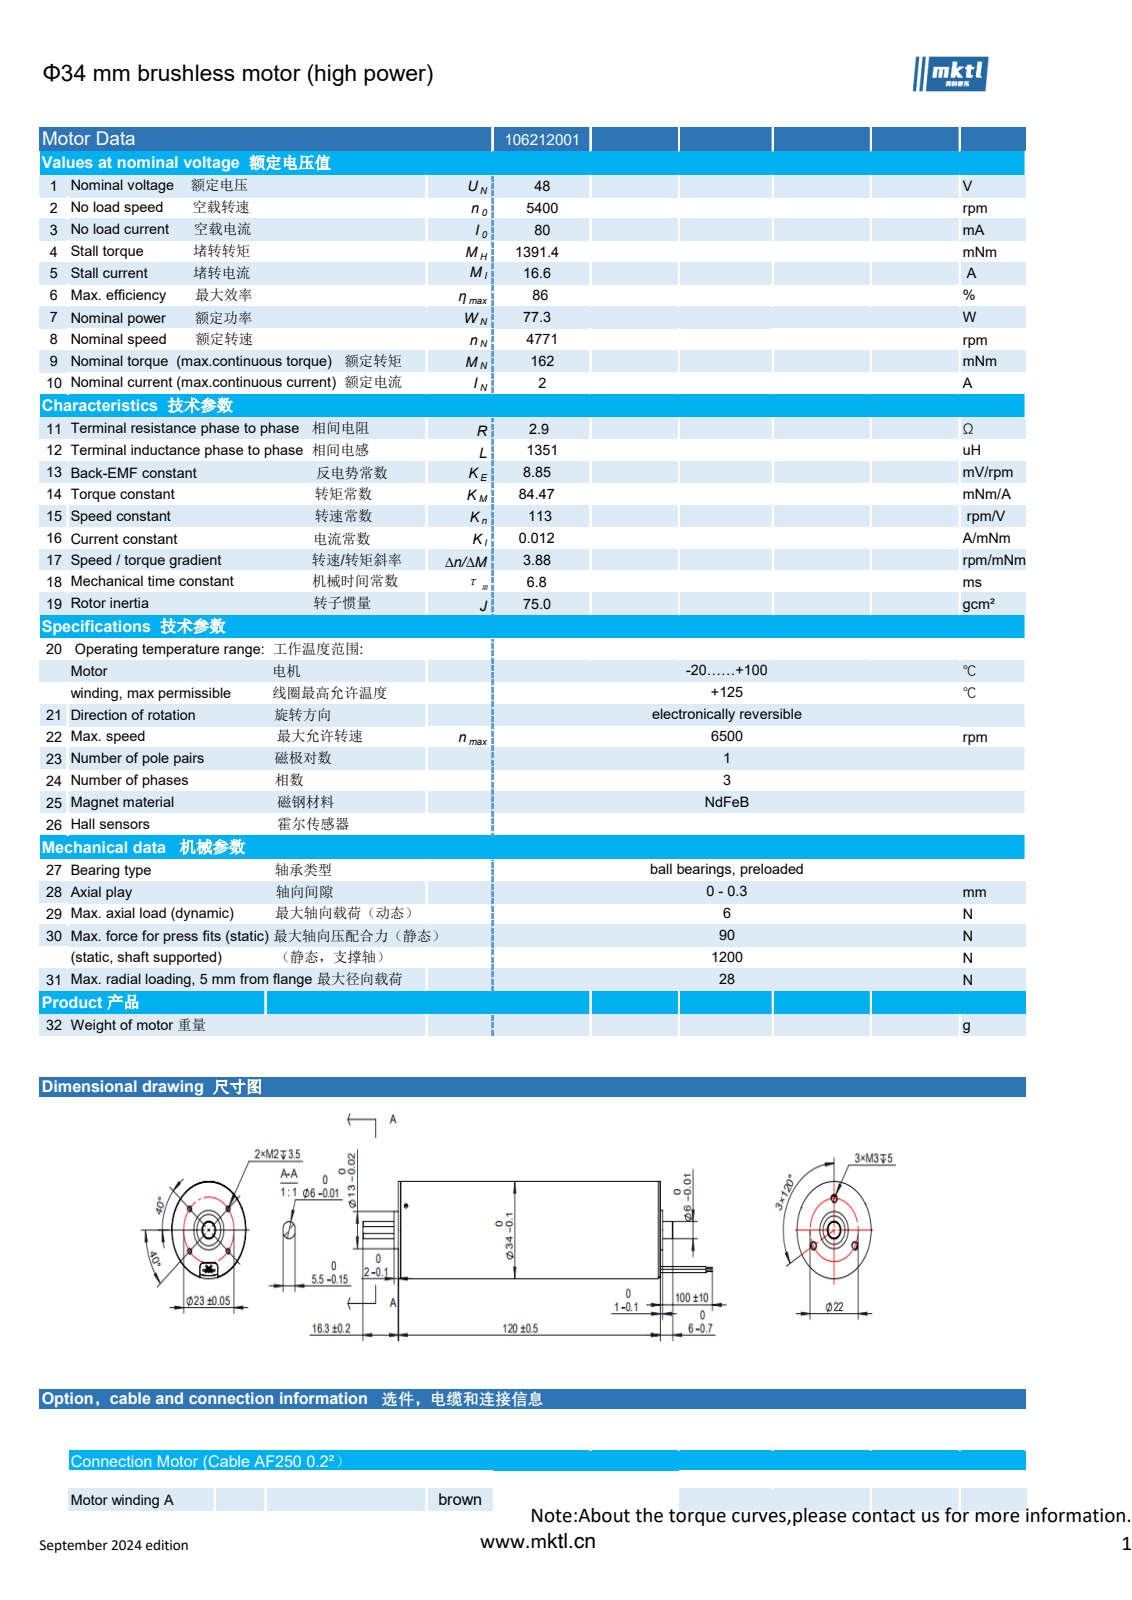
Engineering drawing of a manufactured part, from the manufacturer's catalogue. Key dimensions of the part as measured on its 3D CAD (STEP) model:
Part name (STEP PRODUCT): approval 106212001
STEP written by: SolidWorks 2018 (CONFIG_CONTROL_DESIGN)
Units: millimetres
Bodies: 21 solids, 341 faces (92 planar, 202 cylindrical, 47 other)
Overall size (bounding box): 160.05 × 34 × 34
Volume: 56 076 mm³ · Surface area: 68 127 mm²
Round holes (diameter × count): ⌀1.6 ×8, ⌀0.8 ×5, ⌀2.5 ×3, ⌀0.6 ×2, ⌀6 ×1, ⌀10 ×1, ⌀11 ×1, ⌀13 ×1, ⌀15 ×1, ⌀18.5 ×1, ⌀20 ×1, ⌀23.8 ×1
Round bosses / shafts (diameter × count): ⌀1 ×8, ⌀0.5 ×7, ⌀1.2 ×2, ⌀34 ×1, ⌀32 ×1, ⌀31.9 ×1, ⌀31.8 ×1, ⌀16 ×1
Partial cylindrical surfaces — rounded edges, fillets, slot ends (radius × count): R0.2 ×7, R1.3 ×4, R0.5 ×3, R1.5 ×2
Main face-to-face distances: 109.2, 120, 3, 10.8, 6.5, 4.3, 113.5, 1, 119, 5
Hole centre spacings: 11.5, 2, 11, 14.25, 1.99, 2.02, 2.48, 3.85
